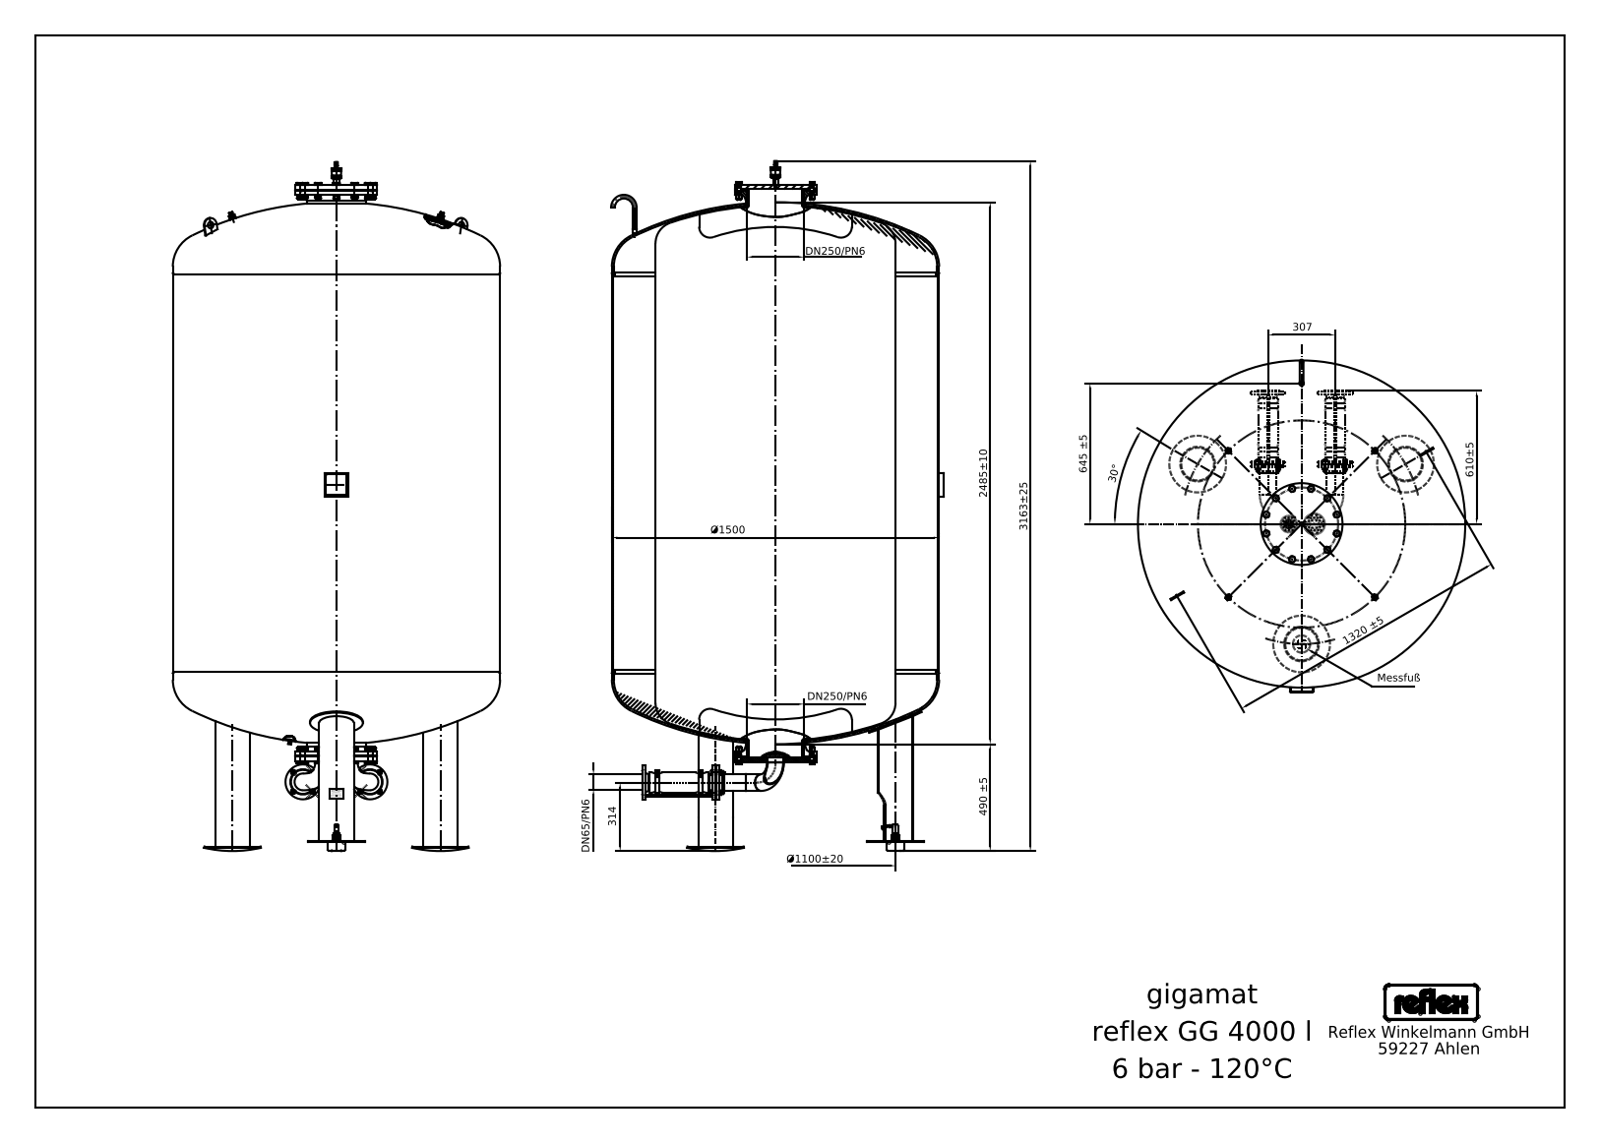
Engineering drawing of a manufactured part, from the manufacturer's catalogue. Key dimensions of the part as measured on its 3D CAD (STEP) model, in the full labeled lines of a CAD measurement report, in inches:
STEP written by: Mechanical Desktop 2008 (CONFIG_CONTROL_DESIGN)
Units: inches
Bodies: 24 solids, 1027 faces (532 planar, 258 cylindrical, 237 other)
Overall size (bounding box): 124.528 × 59.055 × 59.055
Volume: 249 300 in³ · Surface area: 36 580 in²
Round holes (diameter × count): ⌀0.551 ×8, ⌀0.315 ×1, ⌀0.787 ×1, ⌀1.181 ×1, ⌀2.768 ×1, ⌀2.996 ×1, ⌀5.906 ×1, ⌀10.252 ×1
Round bosses / shafts (diameter × count): ⌀0.63 ×24, ⌀6.26 ×3, ⌀6.299 ×2, ⌀3.783 ×2, ⌀3.39 ×2, ⌀2.996 ×2, ⌀0.654 ×2, ⌀0.472 ×2
Partial cylindrical surfaces — rounded edges, fillets, slot ends (radius × count): R0.079 ×8, R0.332 ×4, R0.133 ×3, R0.227 ×2, R0.398 ×2, R0.548 ×2, R0.555 ×2, R0.75 ×2
Main face-to-face distances: 71.85, 0.866, 102.244, 1.063, 103.307, 87.165, 15.315, 88.031, 16.181, 0.197
Hole centre spacings: 2.559, 3.619, 12.087, 5.118, 10.435, 12.617, 14.013, 7.888
